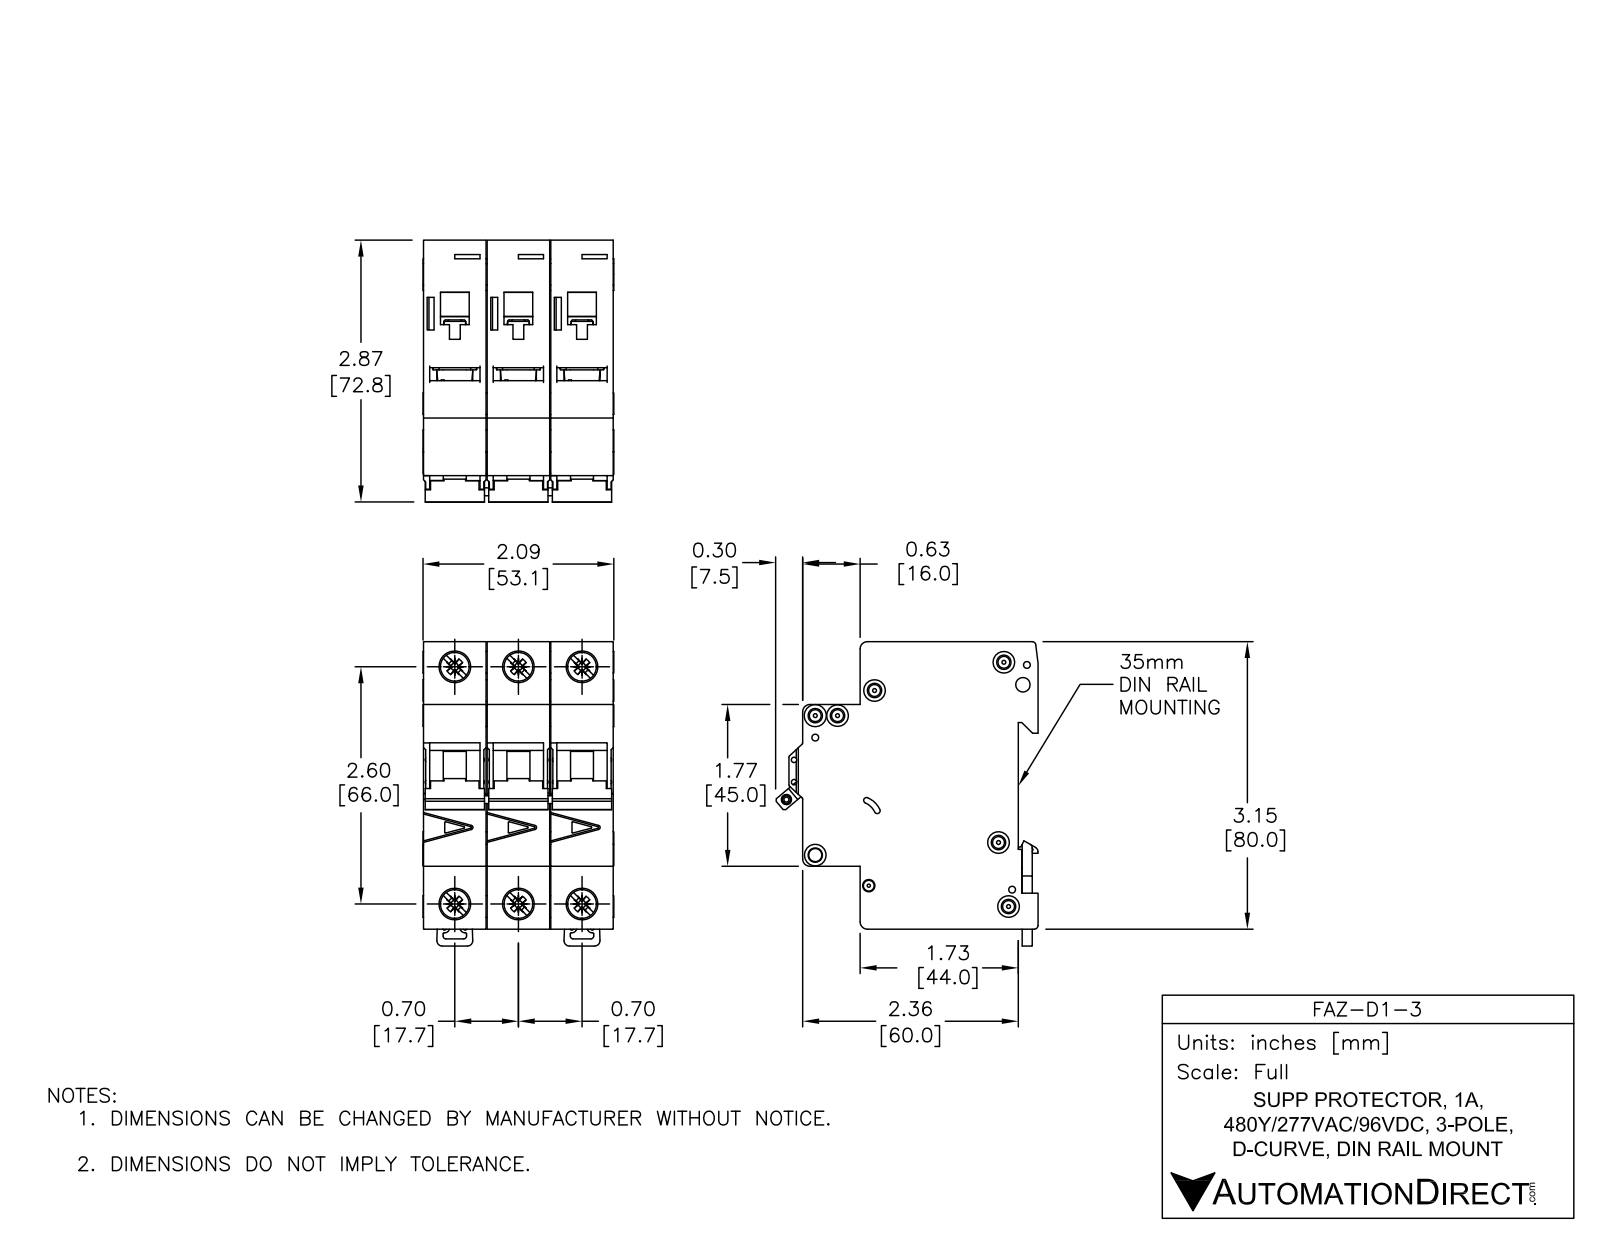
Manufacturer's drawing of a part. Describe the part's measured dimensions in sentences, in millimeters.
The part is named "FAZ-D1-3". Its 3-D file was written by "SolidWorks 2014 (AUTOMOTIVE_DESIGN)". It is 11 solids with 1650 faces: 697 planar, 590 cylindrical and 363 other. Overall it measures 84.78 by 73.04 by 53.1 millimeters. Its volume is 224 680 cubic millimeters and its surface area 58 052 square millimeters. Round holes: 6 of diameter 3.6, 4 of diameter 8.2, 3 of diameter 1.9, 2 of diameter 1.09, 2 of diameter 1.5, 2 of diameter 4, 2 of diameter 7.15, 1 of diameter 2.15, 1 of diameter 2.2, 1 of diameter 2.55, 1 of diameter 3.3, 1 of diameter 3.4. Round bosses or shafts: 4 of diameter 6, 3 of diameter 2.5, 2 of diameter 8.2. Partial cylindrical surfaces (rounded edges, fillets, slot ends): 68 of radius 0.25, 25 of radius 0.5, 12 of radius 1, 12 of radius 2, 11 of radius 0.2, 3 of radius 1.8, 2 of radius 0.8, 2 of radius 3. The main face-to-face distances are 17.7, 17.5, 35.4, 35.2, 52.9, 17.9, 79.48, 5.5, 49.5, 44. The hole center spacings are 17.7, 68.33, 66, 6.2, 13.64, 35.4, 74.89, 4.81.
